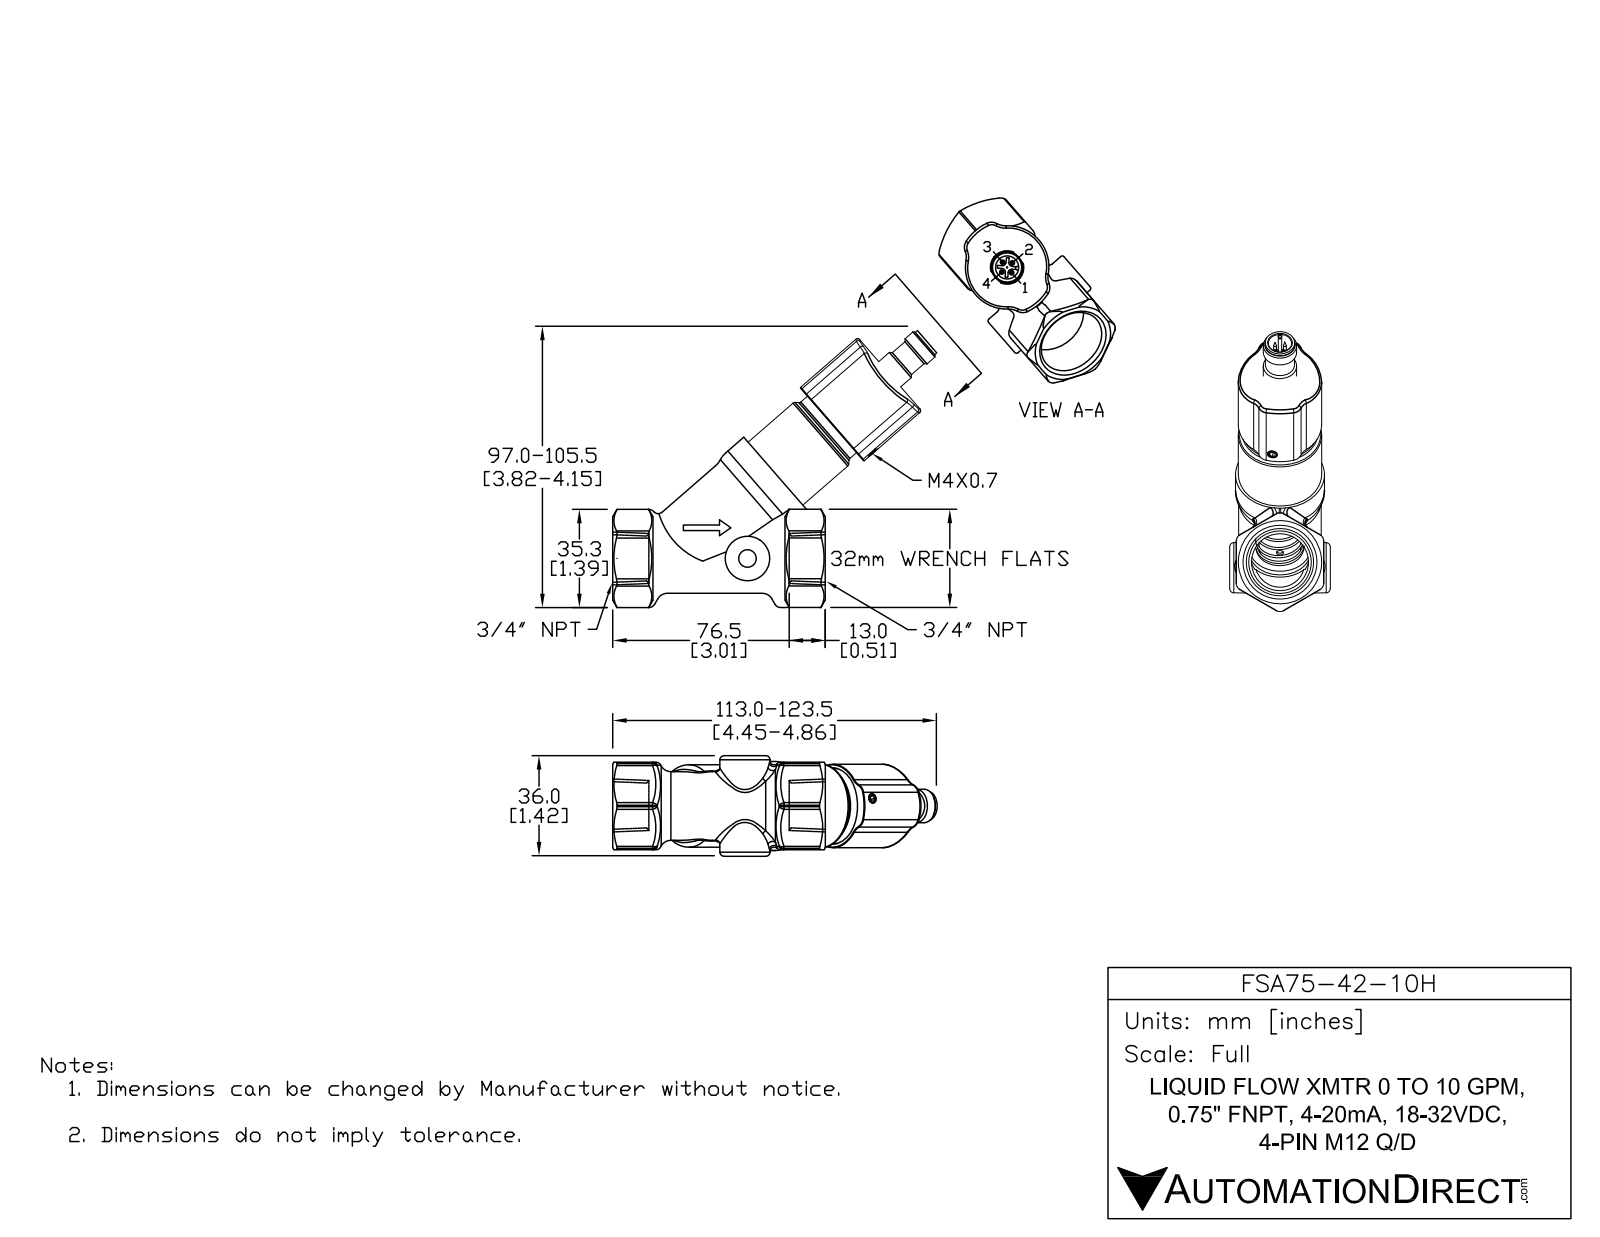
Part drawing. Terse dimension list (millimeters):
name: FSA75-42-10H
written by: SolidWorks 2021 (AUTOMOTIVE_DESIGN)
unit: mm
bodies: 1 solid, 180 faces (60 planar, 86 cylindrical, 34 other)
size: 115 × 104.3 × 35.1
volume: 108 300 mm³; area: 25 350 mm²
holes: 2× ⌀2.5, 2× ⌀7.2, 1× ⌀8.3, 1× ⌀19.5, 1× ⌀24.1
bosses: 1× ⌀32, 1× ⌀30, 1× ⌀27, 1× ⌀12, 1× ⌀10.7, 1× ⌀10.5
rounds: 6× R4, 4× R6, 2× R1, 2× R2, 2× R17.5, 1× R4.8, 1× R14, 1× R14.9
face distances: 31.9, 1.5, 33.5, 35, 20, 44.4, 1.8, 46.2, 7.5, 40.5
hole spacings: 27
